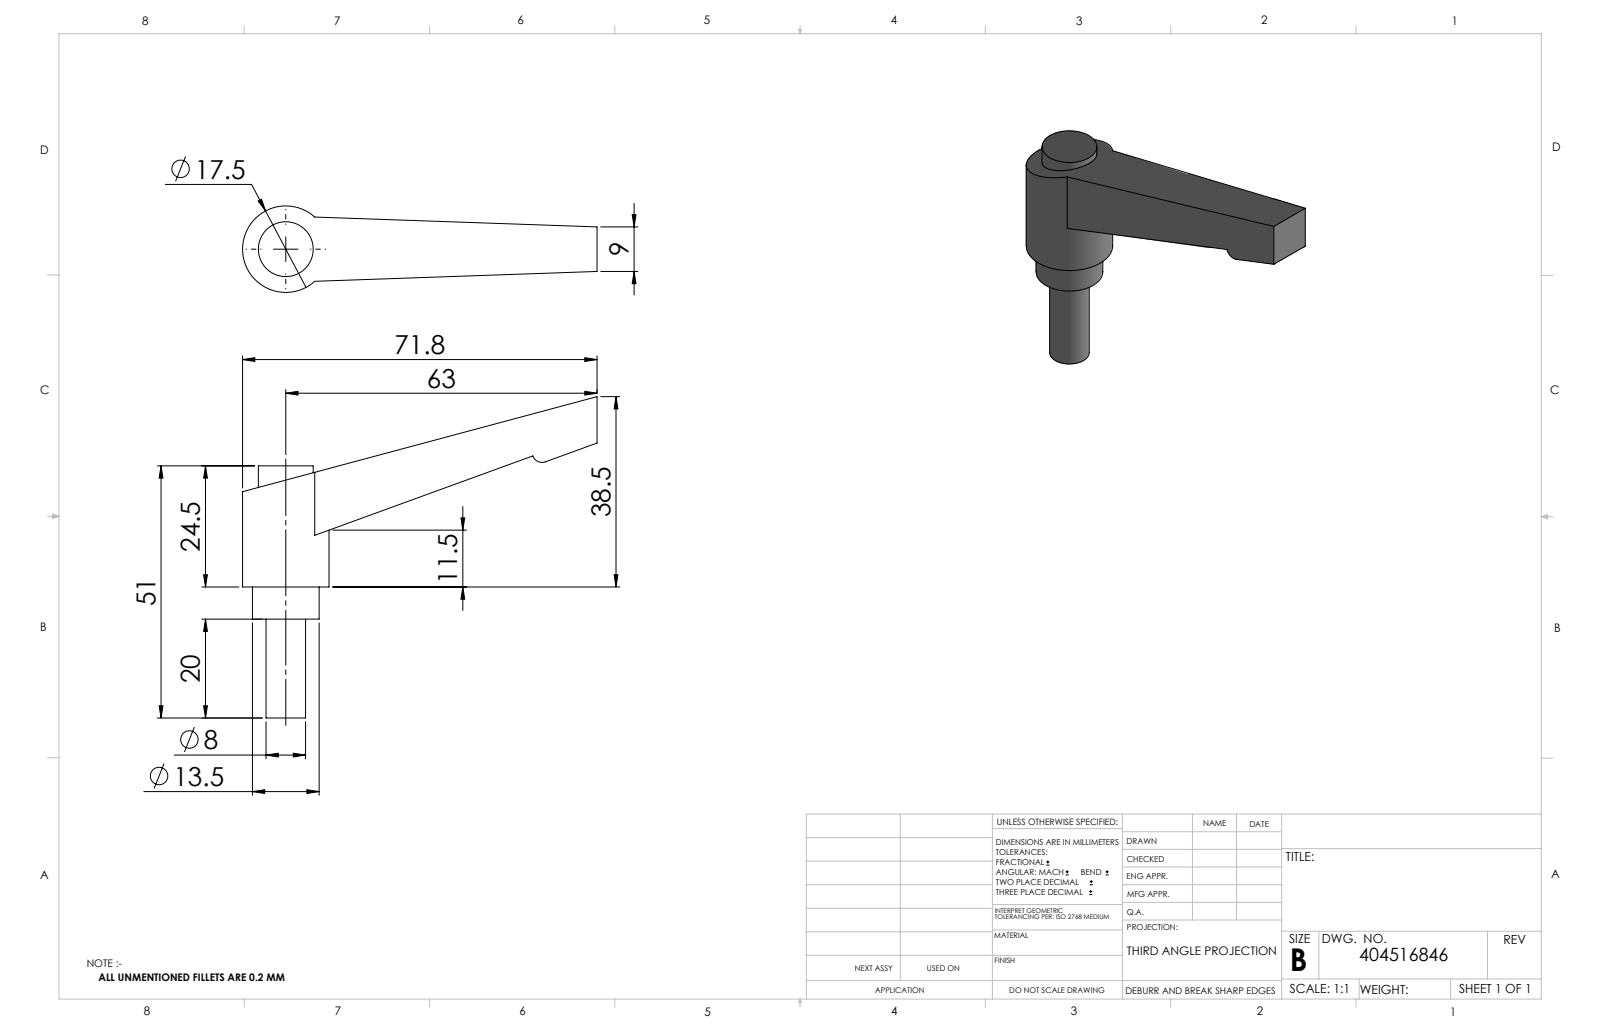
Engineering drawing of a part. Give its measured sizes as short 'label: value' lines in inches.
name: 404516846_c_1
written by: SolidWorks 2014 (CONFIG_CONTROL_DESIGN)
unit: in
bodies: 1 solid, 20 faces (10 planar, 10 cylindrical, 0 other)
size: 2.825 × 2.559 × 0.689
volume: 0.837 in³; area: 7.624 in²
bosses: 1× ⌀0.689, 1× ⌀0.531, 1× ⌀0.437, 1× ⌀0.315
rounds: 1× R0.079
face distances: 0.079, 0.965, 0.256, 1.22, 0.787, 1.043, 2.008
